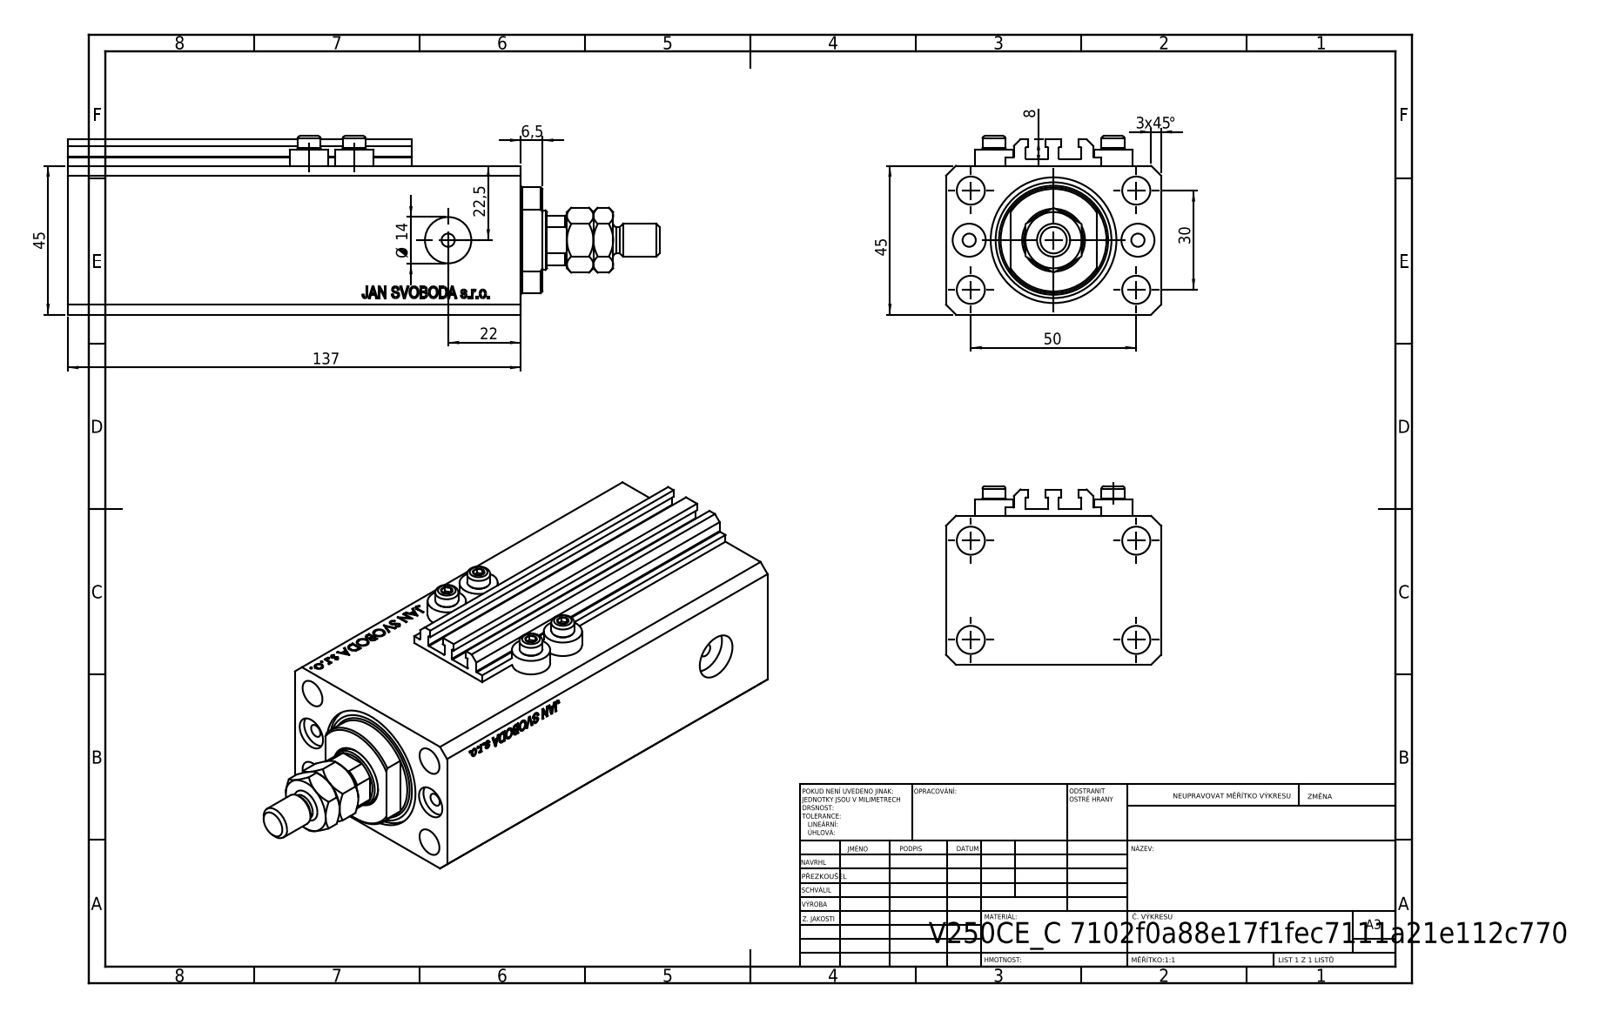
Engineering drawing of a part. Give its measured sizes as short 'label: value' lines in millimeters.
name: MTA; V250CE_C_VCP; V250CE_C_Body; V250CE_VC_C (+1 more)
written by: SolidWorks 2019 (CONFIG_CONTROL_DESIGN)
unit: mm
bodies: 9 solids, 1082 faces (518 planar, 90 cylindrical, 474 other)
size: 178.9 × 65 × 54
volume: 370 563 mm³; area: 94 502 mm²
holes: 8× ⌀4, 5× ⌀8.5, 2× ⌀10, 2× ⌀14, 1× ⌀18, 1× ⌀25, 1× ⌀38
bosses: 4× ⌀11.6, 4× ⌀7, 1× ⌀10, 1× ⌀8
rounds: 10× R0.2, 1× R8.5, 1× R16
face distances: 45, 65, 47, 111.9, 137, 25.1, 2.5, 2, 6, 10
hole spacings: 15.01, 29.15, 52.68, 13.6, 25.5, 30, 36, 38.48
